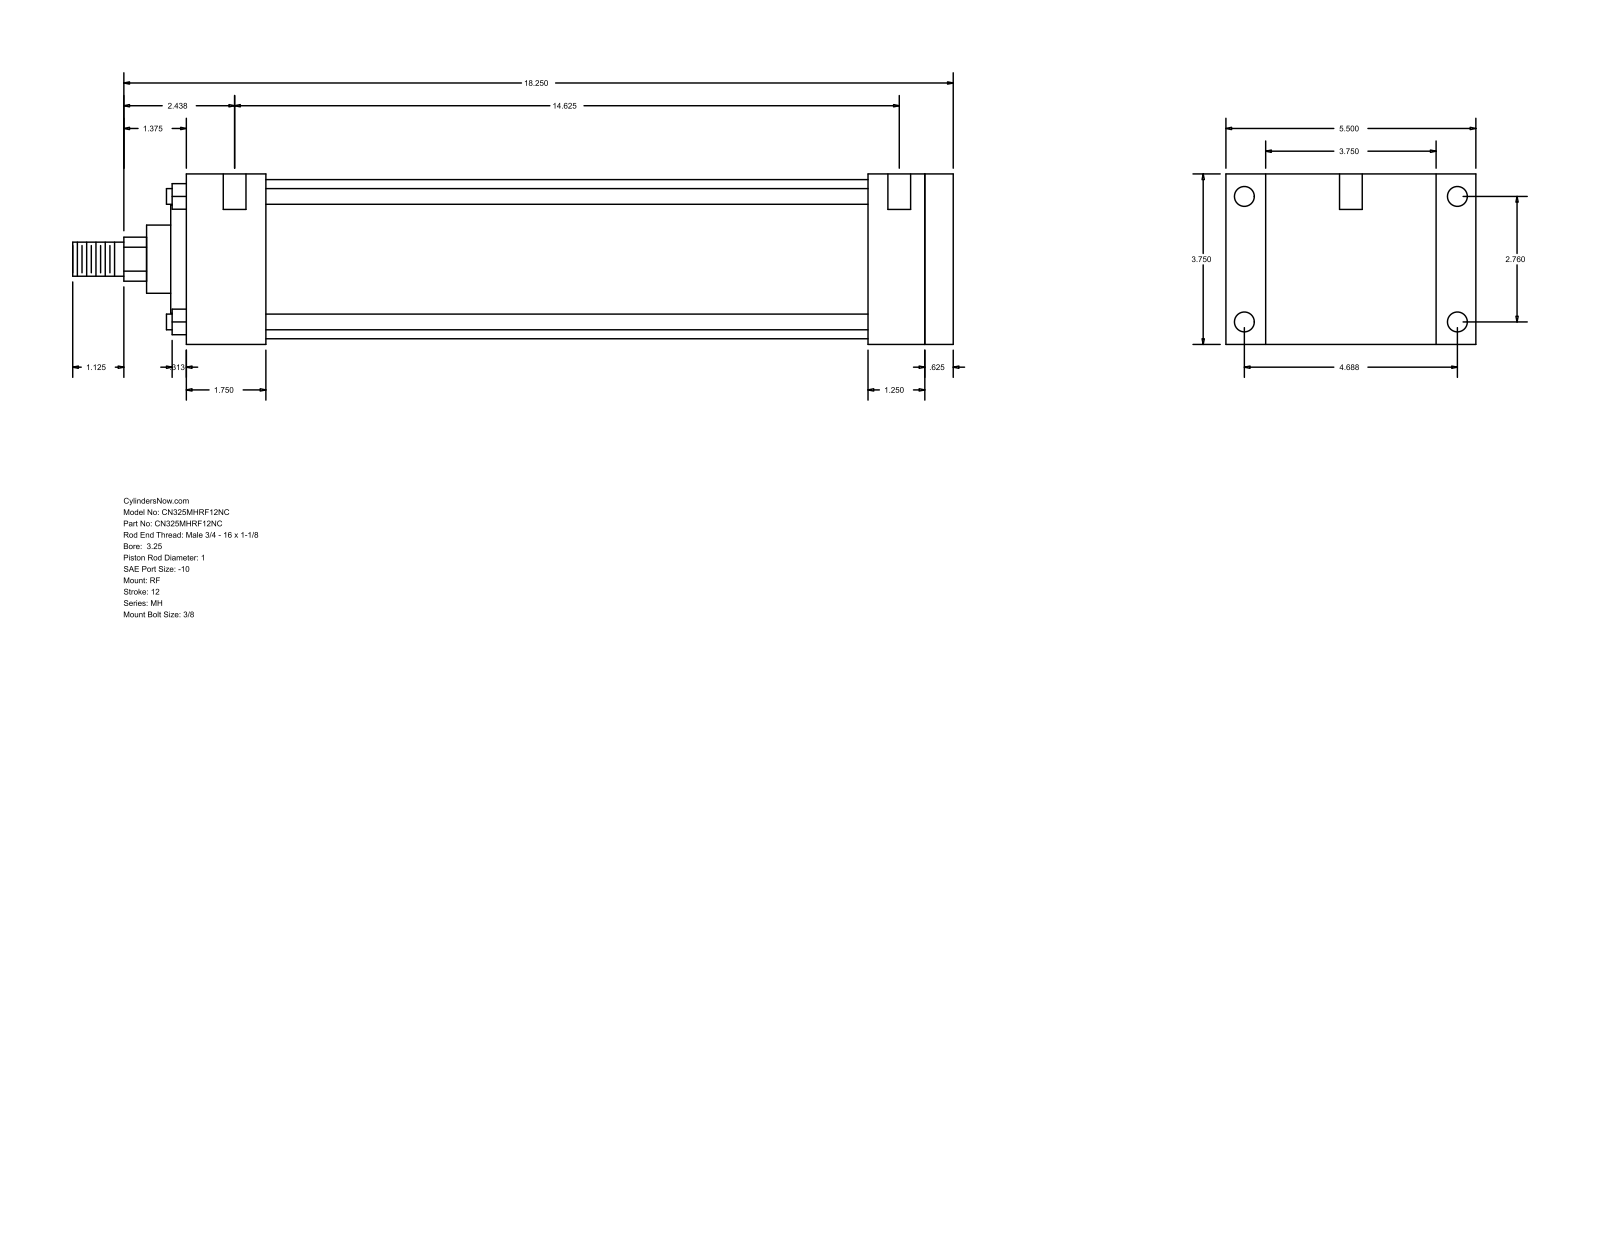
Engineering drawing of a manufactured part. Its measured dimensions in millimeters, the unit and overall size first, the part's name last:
Units: millimetres
Overall size (bounding box): 492.12 × 139.7 × 95.25
Round holes (diameter × count): ⌀5.56 ×4, ⌀11.13 ×4, ⌀12.7 ×2
Round bosses / shafts (diameter × count): ⌀8.76 ×4, ⌀88.9 ×1, ⌀60.33 ×1, ⌀38.1 ×1, ⌀25.4 ×1, ⌀19.05 ×1
Partial cylindrical surfaces — rounded edges, fillets, slot ends (radius × count): R12.29 ×1
Main face-to-face distances: 95.24, 428.63, 412.76, 15.87, 22.23, 117.47, 44.46, 368.3, 384.17, 381.01
Hole centre spacings: 70.1, 119.06, 138.16, 377.82, 1.58, 4.76, 371.48, 373.06
Bodies: 0 solids, 94 faces (65 planar, 29 cylindrical, 0 other)
Part name (STEP PRODUCT): MH_RF__0325_1
STEP written by: GSSL Pune (CONFIG_CONTROL_DESIGN)
